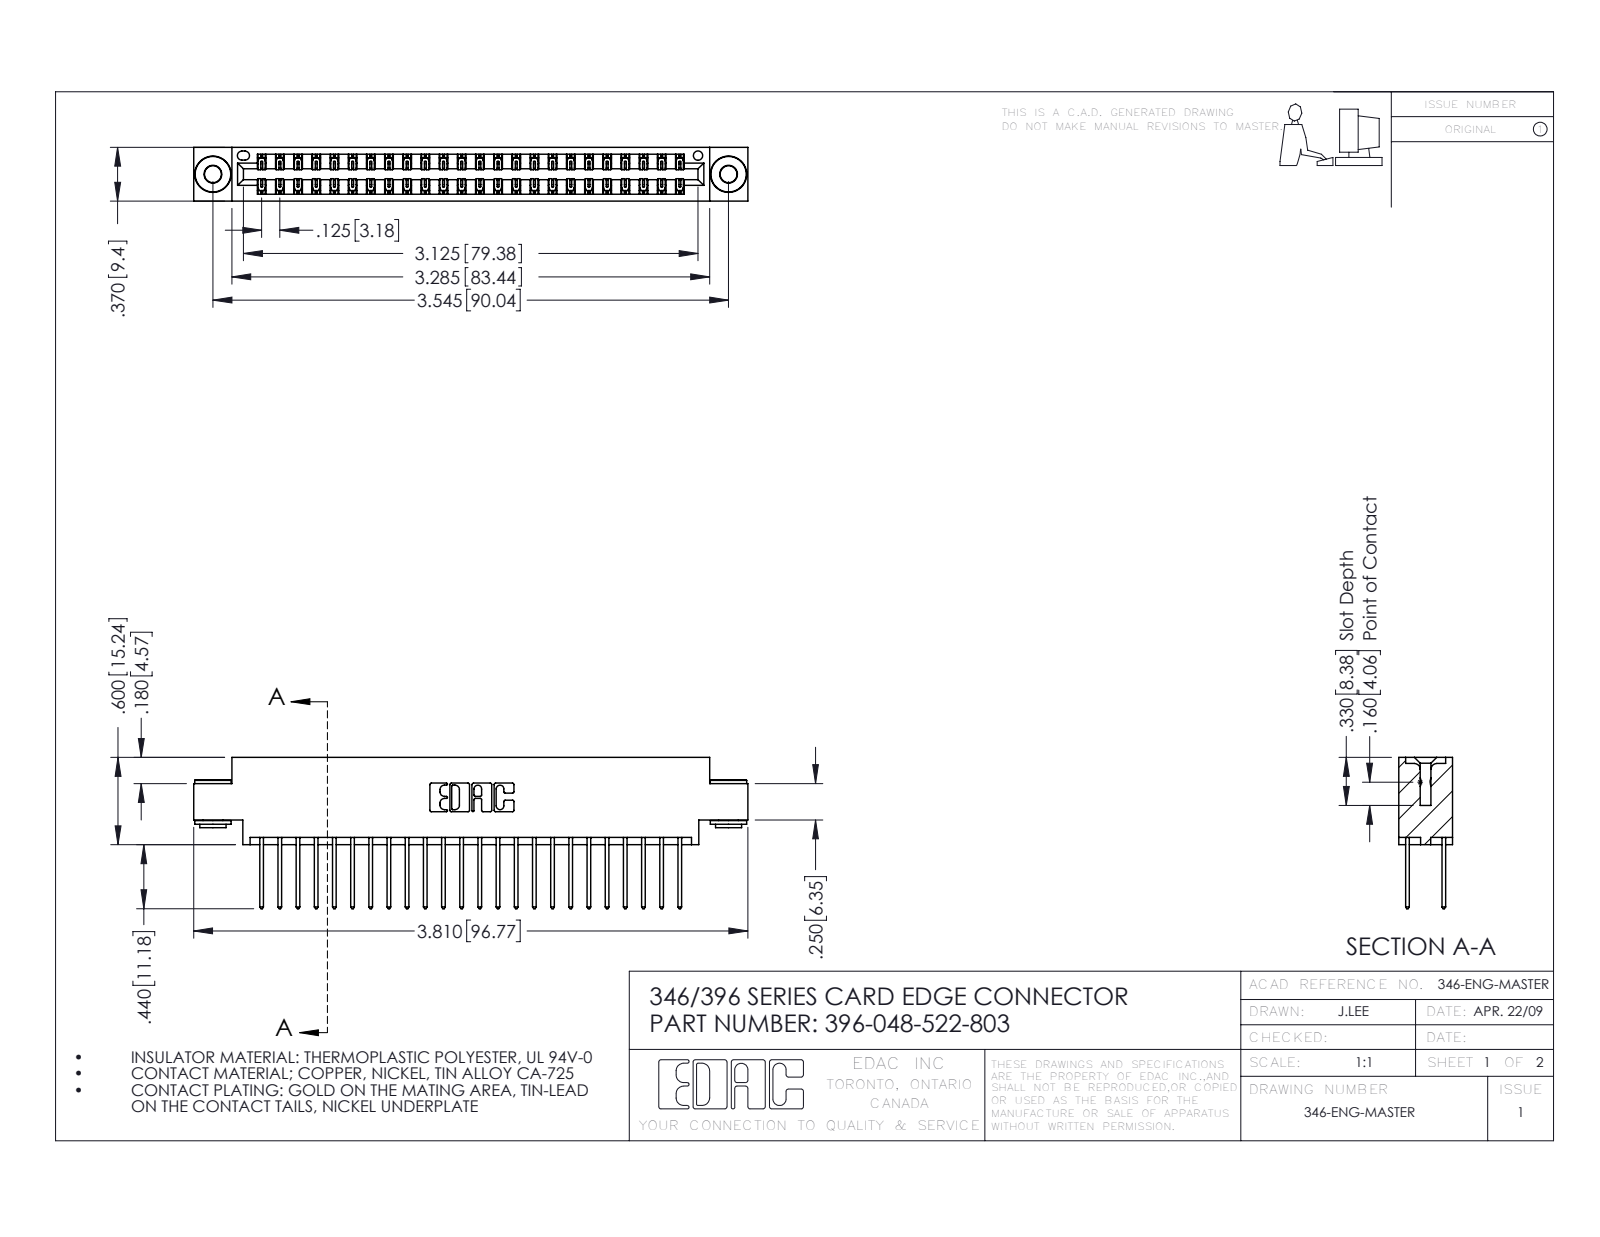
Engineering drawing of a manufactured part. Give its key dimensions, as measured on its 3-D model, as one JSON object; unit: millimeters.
{"part_name": "345-250-002_345-250-002-102; 346 Part_0.170 Offset - 0.156 Dia-TH; 396-048-522-803; 345-292-001_345-293-122", "step_written_by": "SolidWorks 2016 (CONFIG_CONTROL_DESIGN)", "units": "millimeters", "bodies": {"solids": 51, "faces": 2660, "planar": 1770, "cylindrical": 882, "other": 8}, "overall_size": [96.8, 26.4, 9.4], "volume_mm3": 9290, "surface_area_mm2": 13450, "round_holes": [[2.9, 2], [4, 2], [1.6, 1]], "round_bosses_or_shafts": [[6.4, 2], [4.6, 2], [3.5, 2]], "partial_cylinders_radius": [[0.2, 72], [0.3, 48], [0.3, 22], [0.2, 6], [0.8, 6], [0.7, 3], [0.4, 2], [0.6, 2]], "face_to_face_distances": [1.2, 8.2, 6.4, 9.4, 0.6, 1.8, 7.6, 7, 3.8, 5.6], "hole_center_spacings": [6.2, 84.8, 90]}
